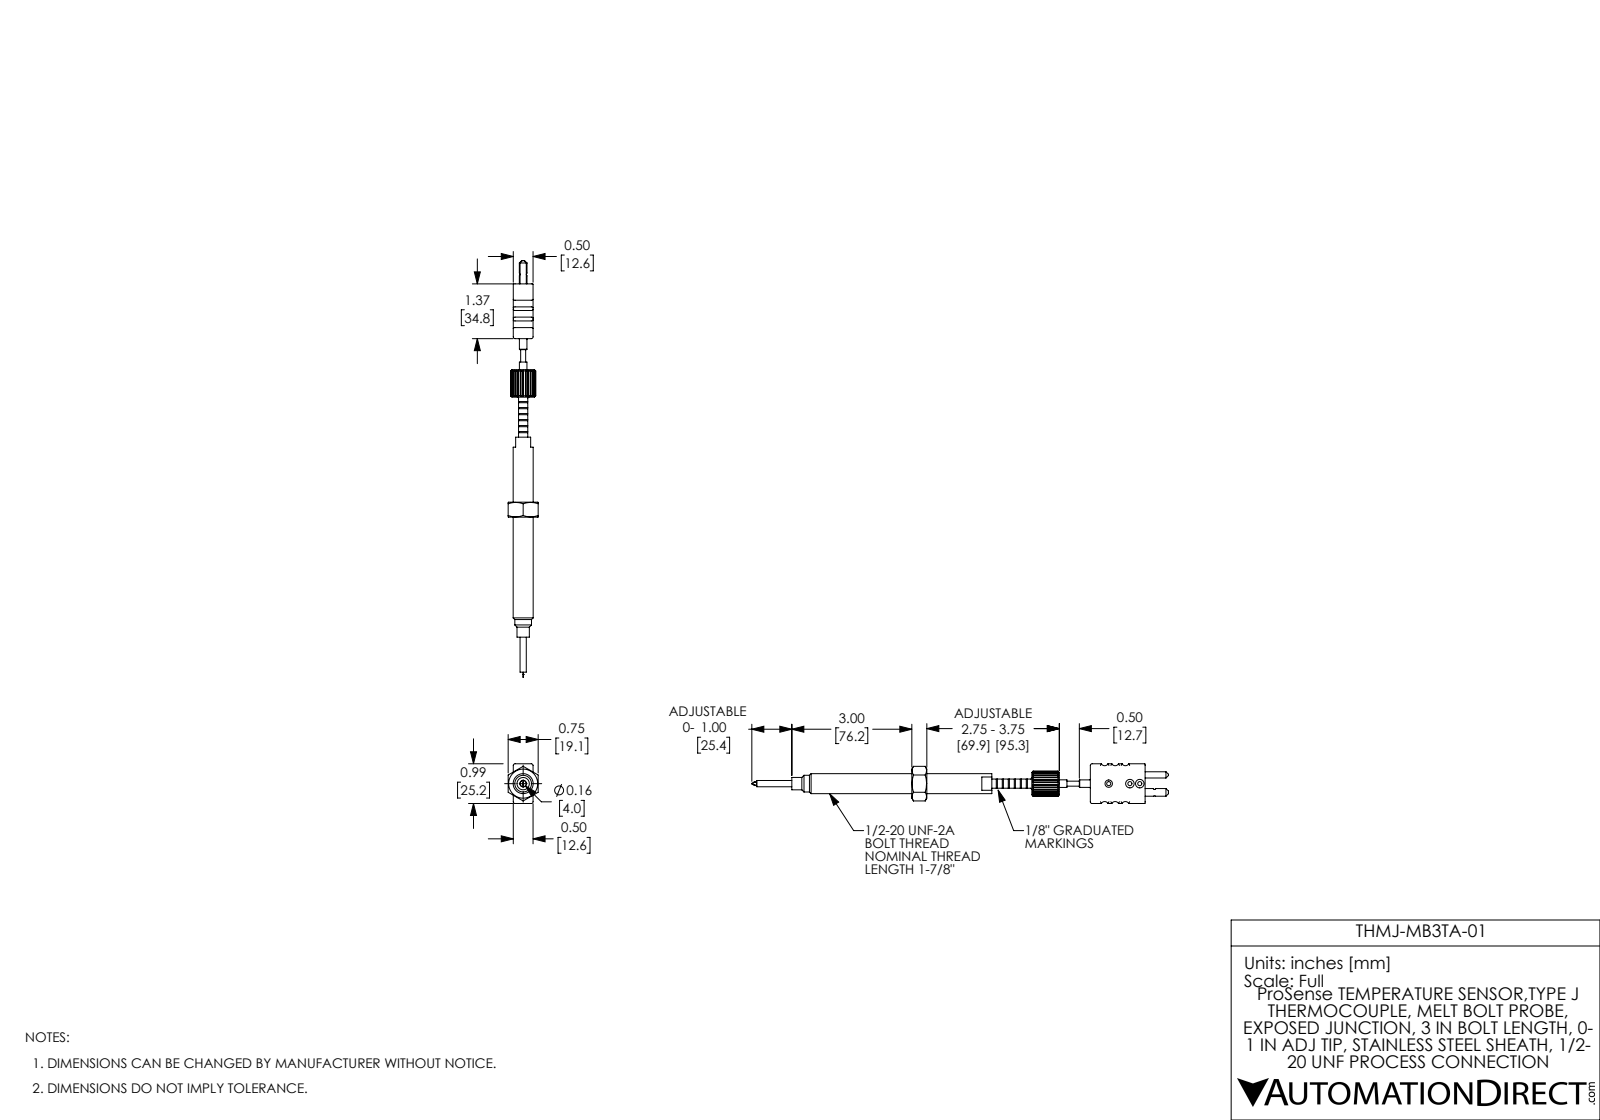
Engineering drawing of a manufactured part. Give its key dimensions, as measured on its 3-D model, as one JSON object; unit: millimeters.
{"part_name": "THMJ-MB3TA-01", "step_written_by": "SolidWorks 2017 (AUTOMOTIVE_DESIGN)", "units": "millimeters", "bodies": {"solids": 4, "faces": 372, "planar": 145, "cylindrical": 125, "other": 102}, "overall_size": [264.5, 25.2, 19.1], "volume_mm3": 32450, "surface_area_mm2": 13010, "round_holes": [[2.6, 2], [4, 2], [3.2, 1], [4.2, 1], [4.7, 1], [7.5, 1], [7.8, 1]], "round_bosses_or_shafts": [[4, 2], [0.4, 2], [12.7, 1], [10.6, 1], [7.9, 1], [7.8, 1], [7.1, 1], [5.8, 1]], "partial_cylinders_radius": [[1.1, 8], [2.4, 6], [0.3, 4], [8, 1]], "face_to_face_distances": [12.6, 19.1, 25.2, 7.6, 9.5, 3.2, 15.8, 34.8, 25.4, 42.9], "hole_center_spacings": [5.5, 8.4, 14.5, 6.3, 11, 13.4, 19.7]}
